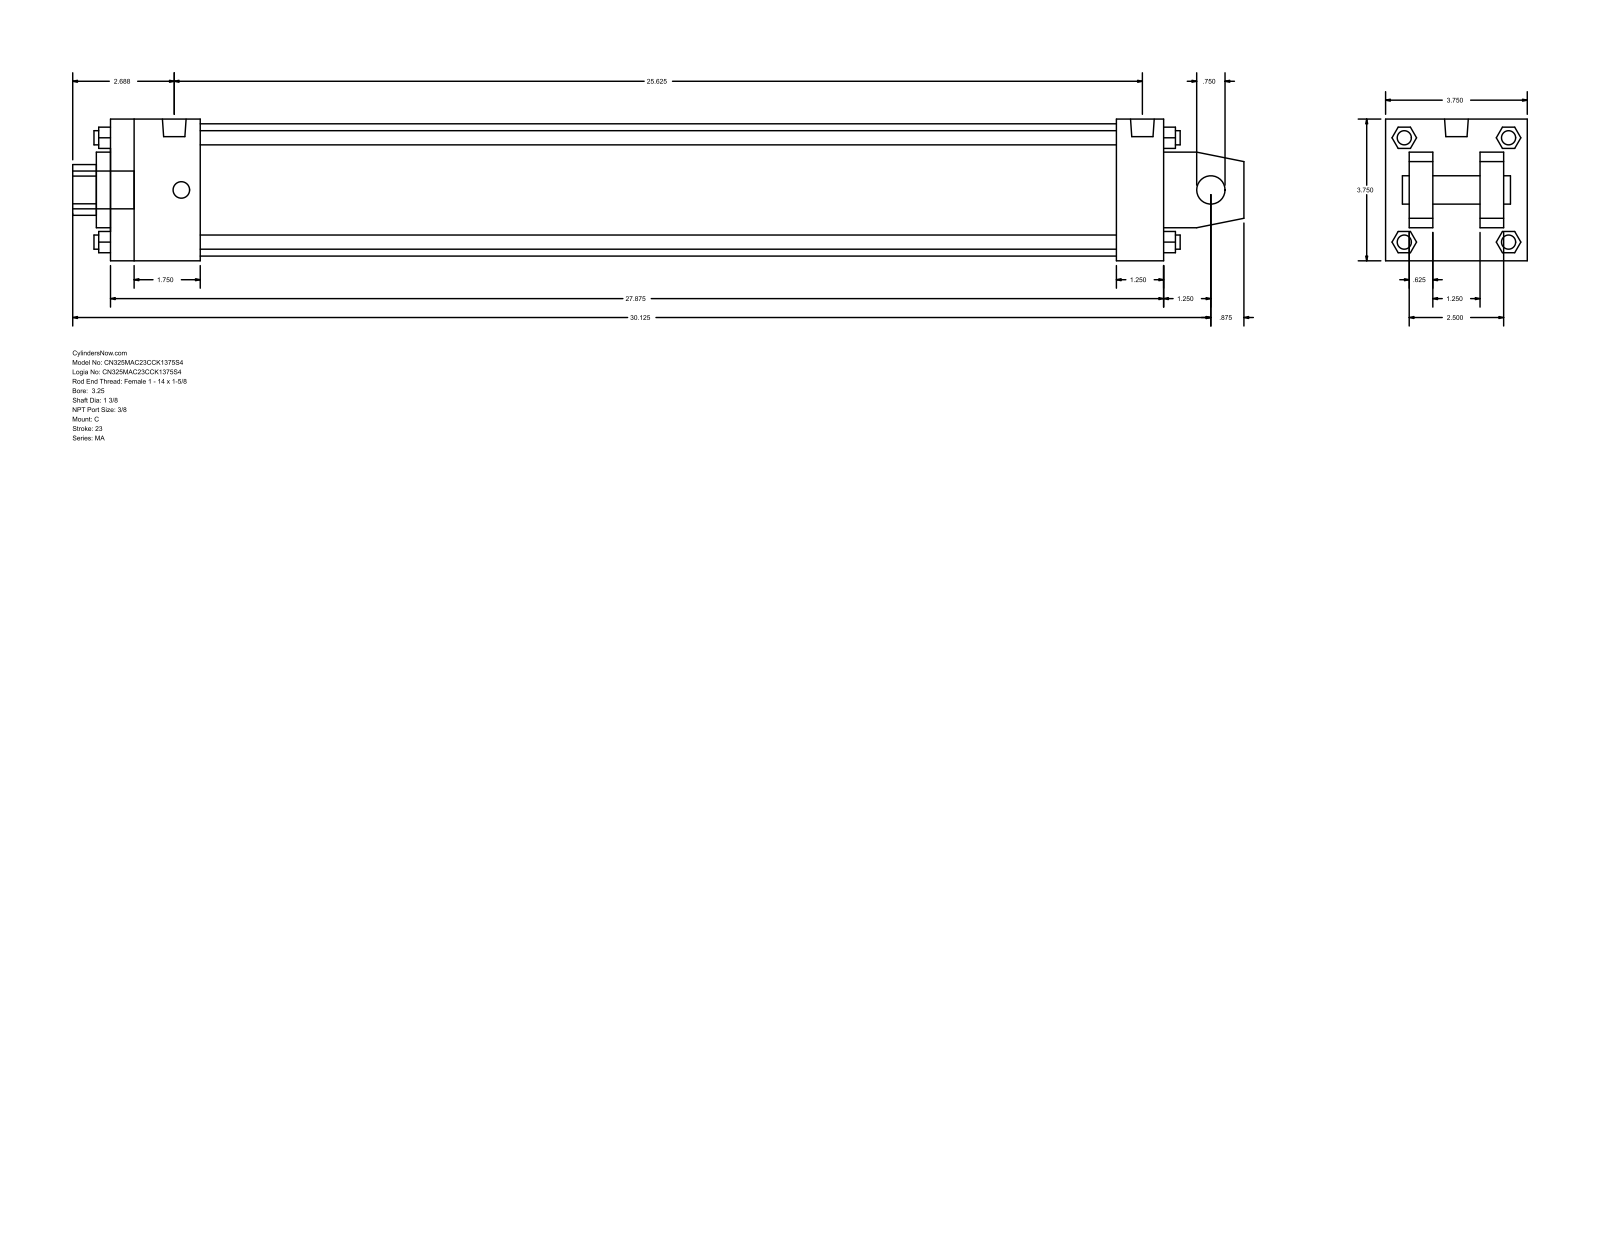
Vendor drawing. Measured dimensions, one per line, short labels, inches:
name: MA_C__0325_1.375
written by: GSSL Pune (CONFIG_CONTROL_DESIGN)
unit: in
bodies: 0 solids, 139 faces (108 planar, 31 cylindrical, 0 other)
size: 31 × 3.75 × 3.75
holes: 1× ⌀0.75, 1× ⌀1.375, 1× ⌀2, 1× ⌀3.5
bosses: 4× ⌀0.437, 4× ⌀0.375, 2× ⌀0.627, 1× ⌀1
rounds: 1× R0.672
face distances: 3.75, 0.625, 2.5, 27.875, 1.25, 3.125, 1.875, 26.625, 1.25, 2.375
